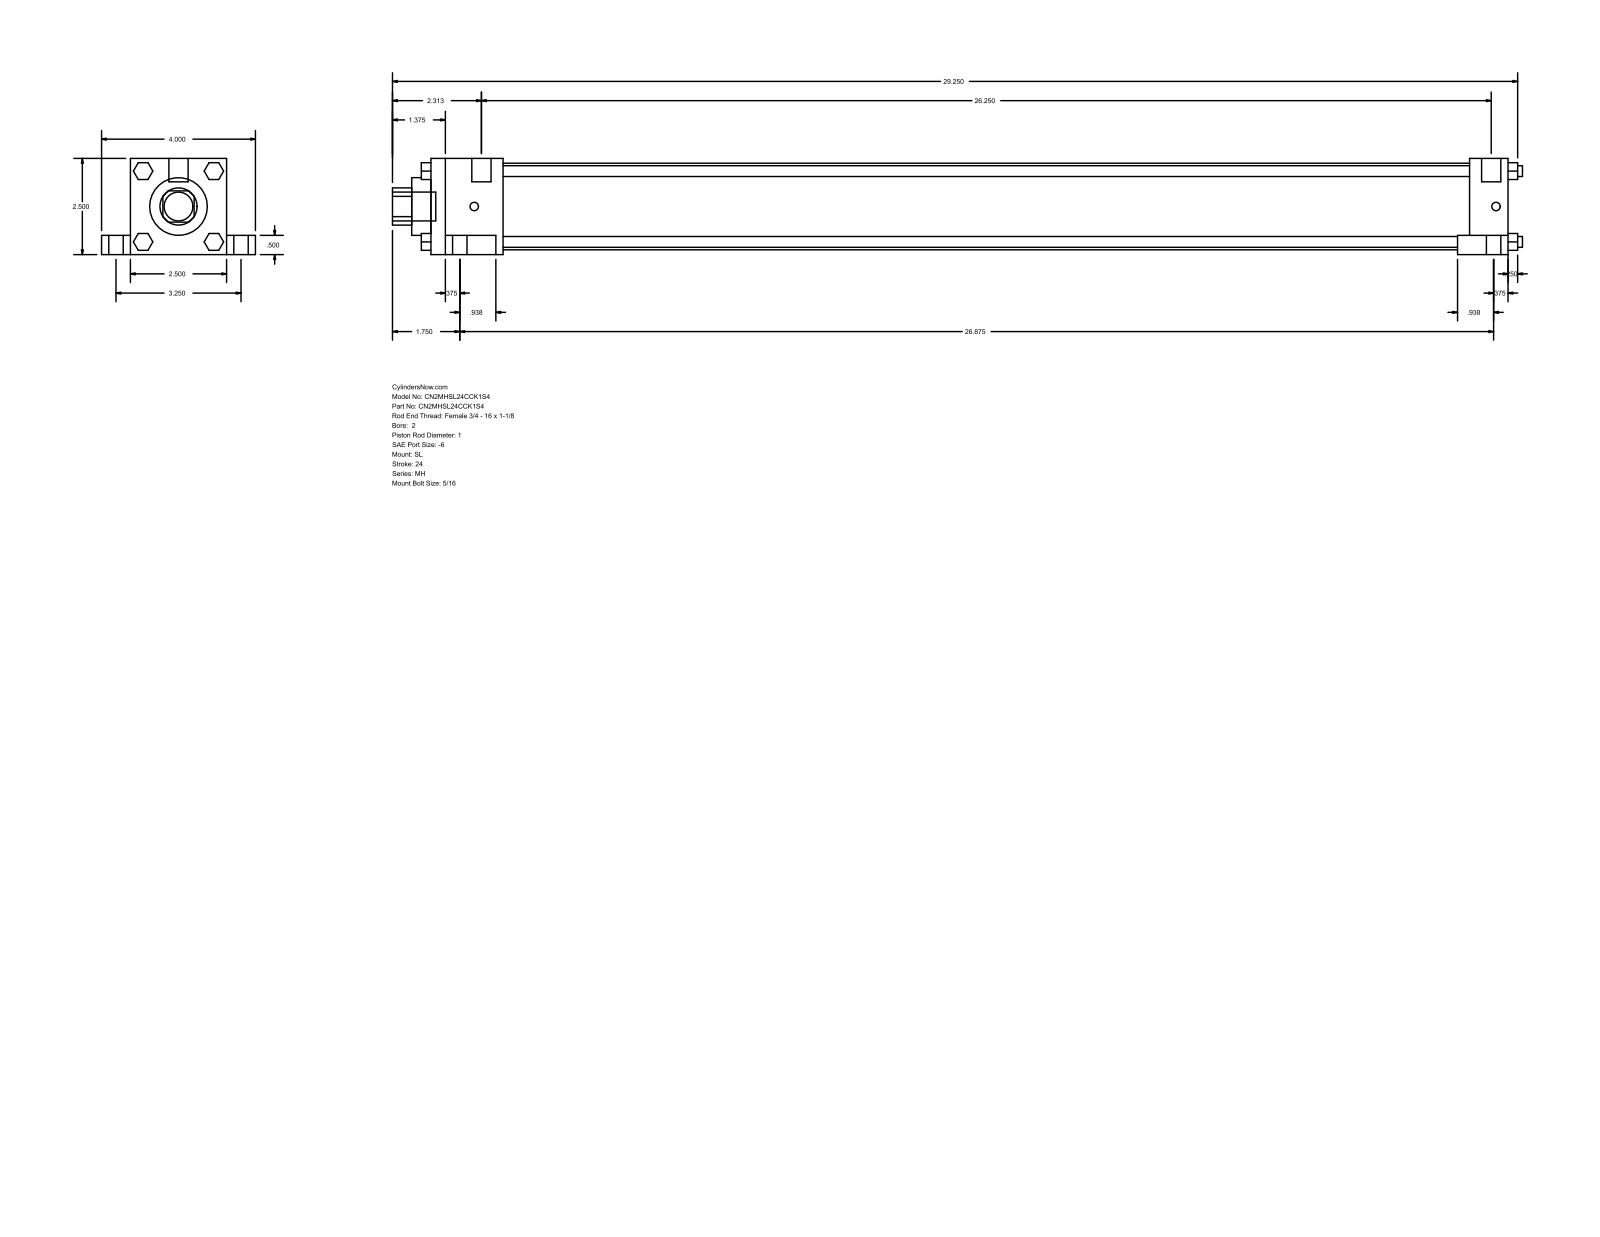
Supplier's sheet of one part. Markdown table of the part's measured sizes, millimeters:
| quantity | value |
| --- | --- |
| part name | MH_SL__0200_1 |
| STEP written by | GSSL Pune (CONFIG_CONTROL_DESIGN) |
| units | millimeters |
| bodies | 0 solids, 148 faces (112 planar, 36 cylindrical, 0 other) |
| overall size | 746.12 × 101.6 × 63.5 |
| round holes (diameter × count) | 25.4 × 1, 38.1 × 1, 57.15 × 1 |
| round bosses / shafts (diameter × count) | 15.88 × 4, 9.53 × 4, 7.14 × 4, 5.56 × 4, 12.7 × 2, 19.05 × 1 |
| partial cylindrical surfaces (radius × count) | 12.29 × 1 |
| main face-to-face distances | 63.5, 711.2, 12.7, 19.05, 50.8, 82.55, 9.52, 25.4, 685.8, 47.63 |
